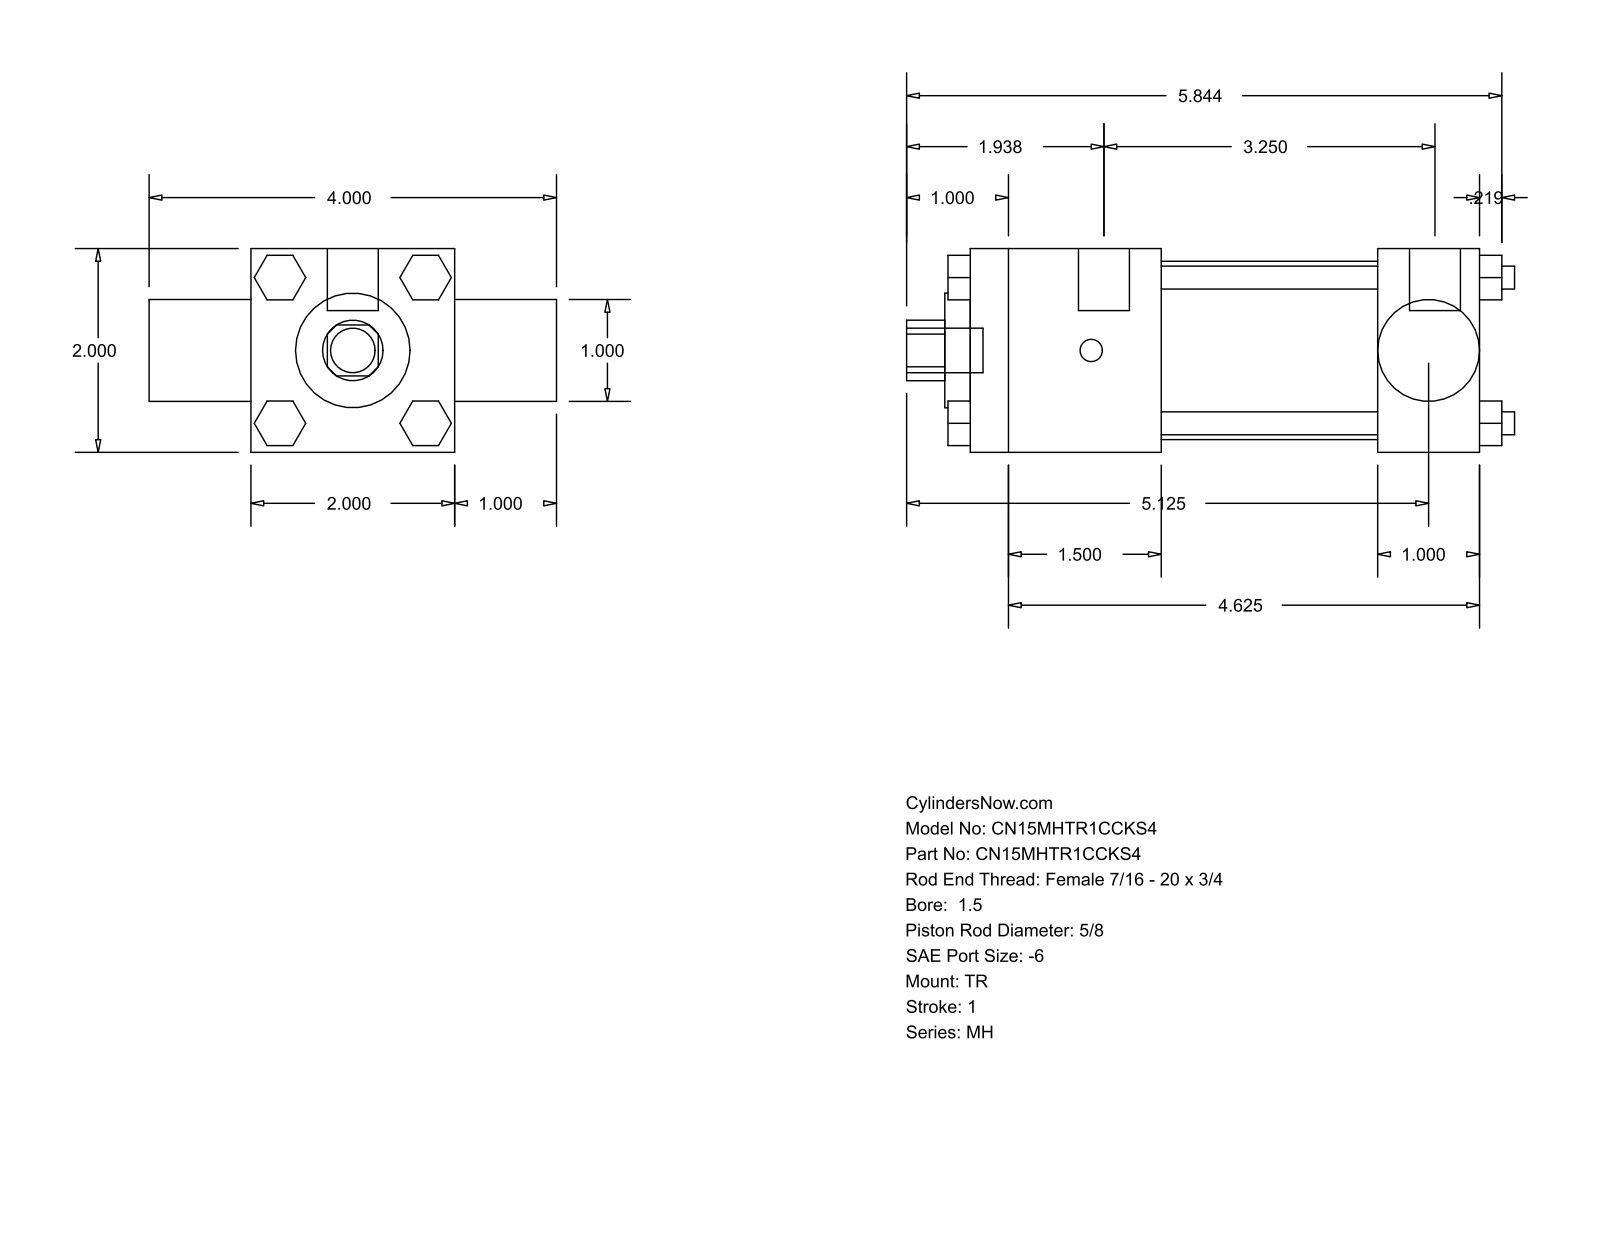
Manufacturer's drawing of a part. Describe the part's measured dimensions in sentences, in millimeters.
The part is named "MH_TR__0150_0.625". Its 3-D file was written by "GSSL Pune (CONFIG_CONTROL_DESIGN)". It is 0 solids with 120 faces: 92 planar, 28 cylindrical and 0 other. Overall it measures 151.61 by 101.6 by 50.8 millimeters. Round holes: 1 of diameter 15.88, 1 of diameter 25.35, 1 of diameter 28.57, 1 of diameter 44.45. Round bosses or shafts: 4 of diameter 5.71, 3 of diameter 5.56, 2 of diameter 12.7, 1 of diameter 11.11. Partial cylindrical surfaces (rounded edges, fillets, slot ends): 1 of radius 7.54. The main face-to-face distances are 50.8, 127, 53.97, 25.4, 76.2, 47.62, 79.38, 101.59, 25.41, 11.11.
